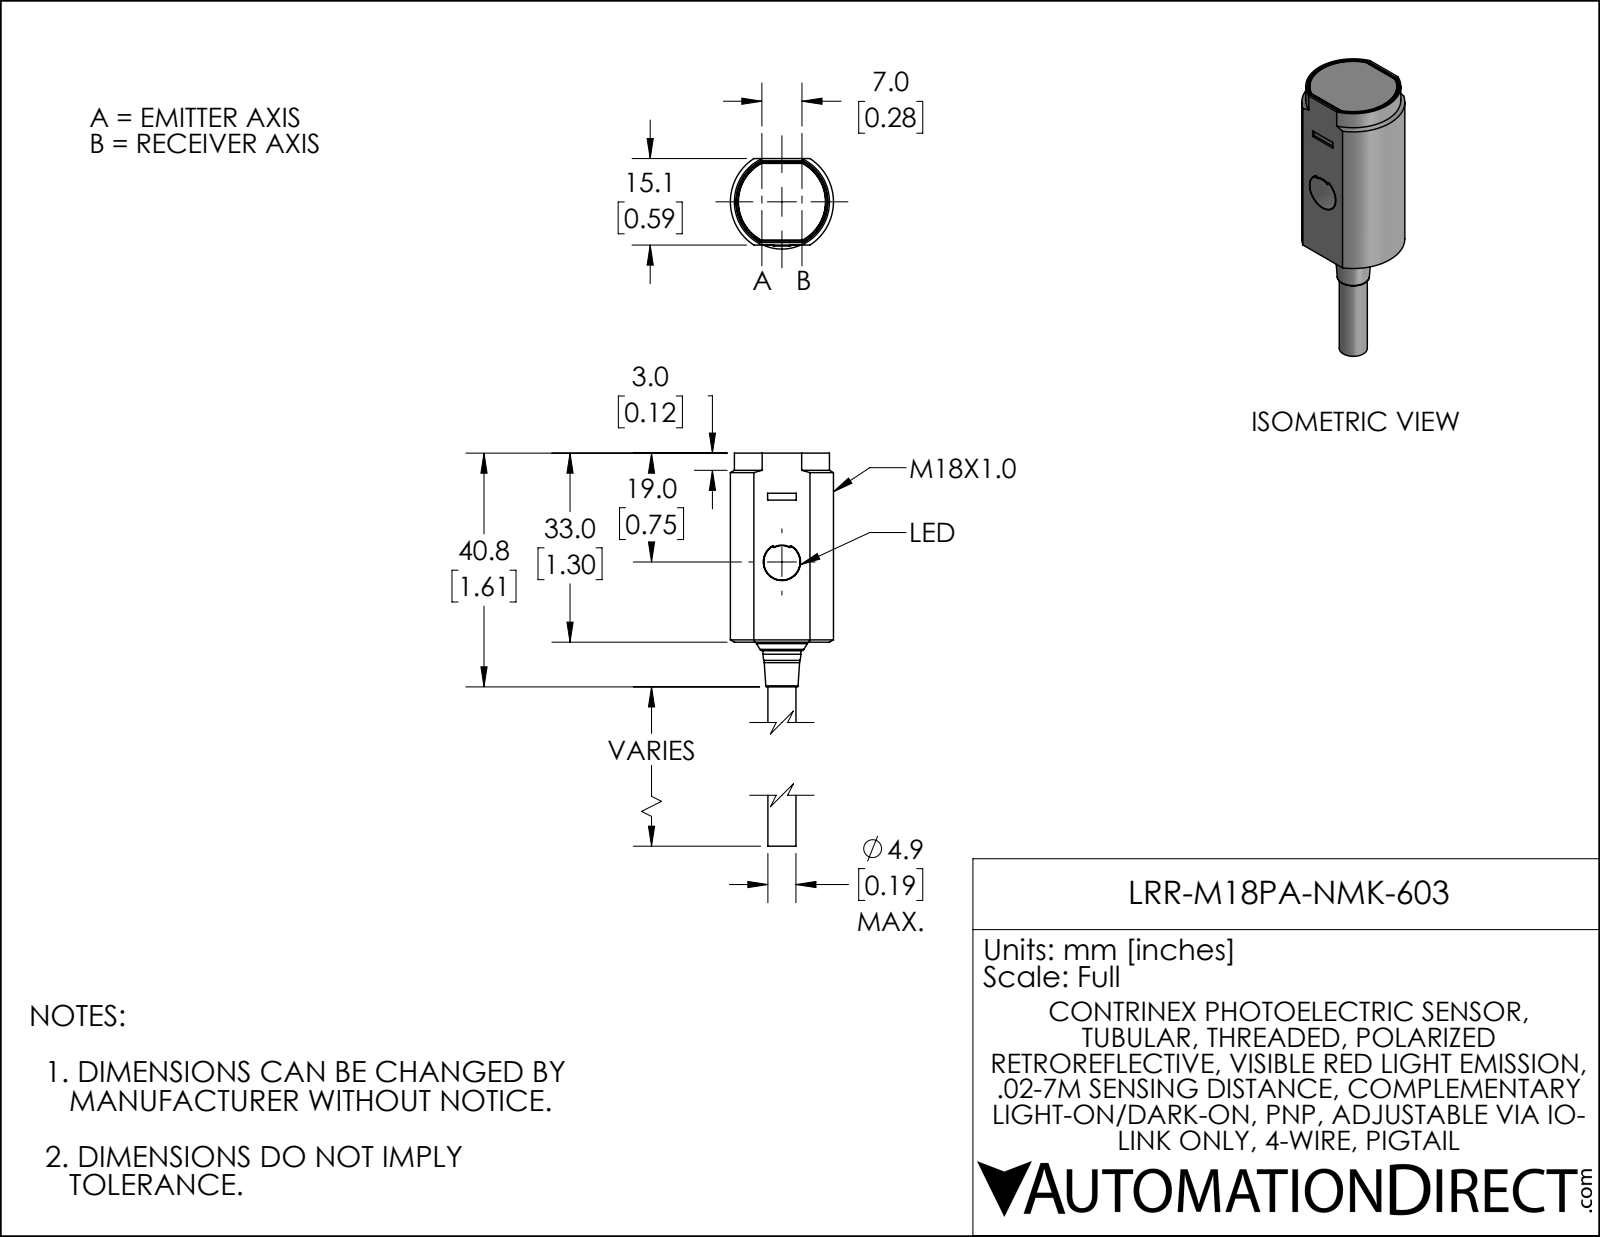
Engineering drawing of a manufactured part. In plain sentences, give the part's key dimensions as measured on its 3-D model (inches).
The part is named "LRR-M18PA-NMK-603". Its 3-D file was written by "SolidWorks 2021 (AUTOMOTIVE_DESIGN)". It is 1 solid with 93 faces: 39 planar, 41 cylindrical and 13 other. Overall it measures 2.205 by 0.709 by 0.622 inches. Its volume is 0.501 cubic inches and its surface area 4.23 square inches. Round holes: 1 of diameter 0.256. Round bosses or shafts: 1 of diameter 0.26, 1 of diameter 0.193. Partial cylindrical surfaces (rounded edges, fillets, slot ends): 8 of radius 0.006, 8 of radius 0.014, 8 of radius 0.028, 1 of radius 0.112, 1 of radius 0.116, 1 of radius 0.299, 1 of radius 0.302, 1 of radius 0.313. The main face-to-face distances are 0.594, 1.297, 1.299, 0.016, 2.205, 2.203, 0.906, 0.579, 0.014, 0.563.
